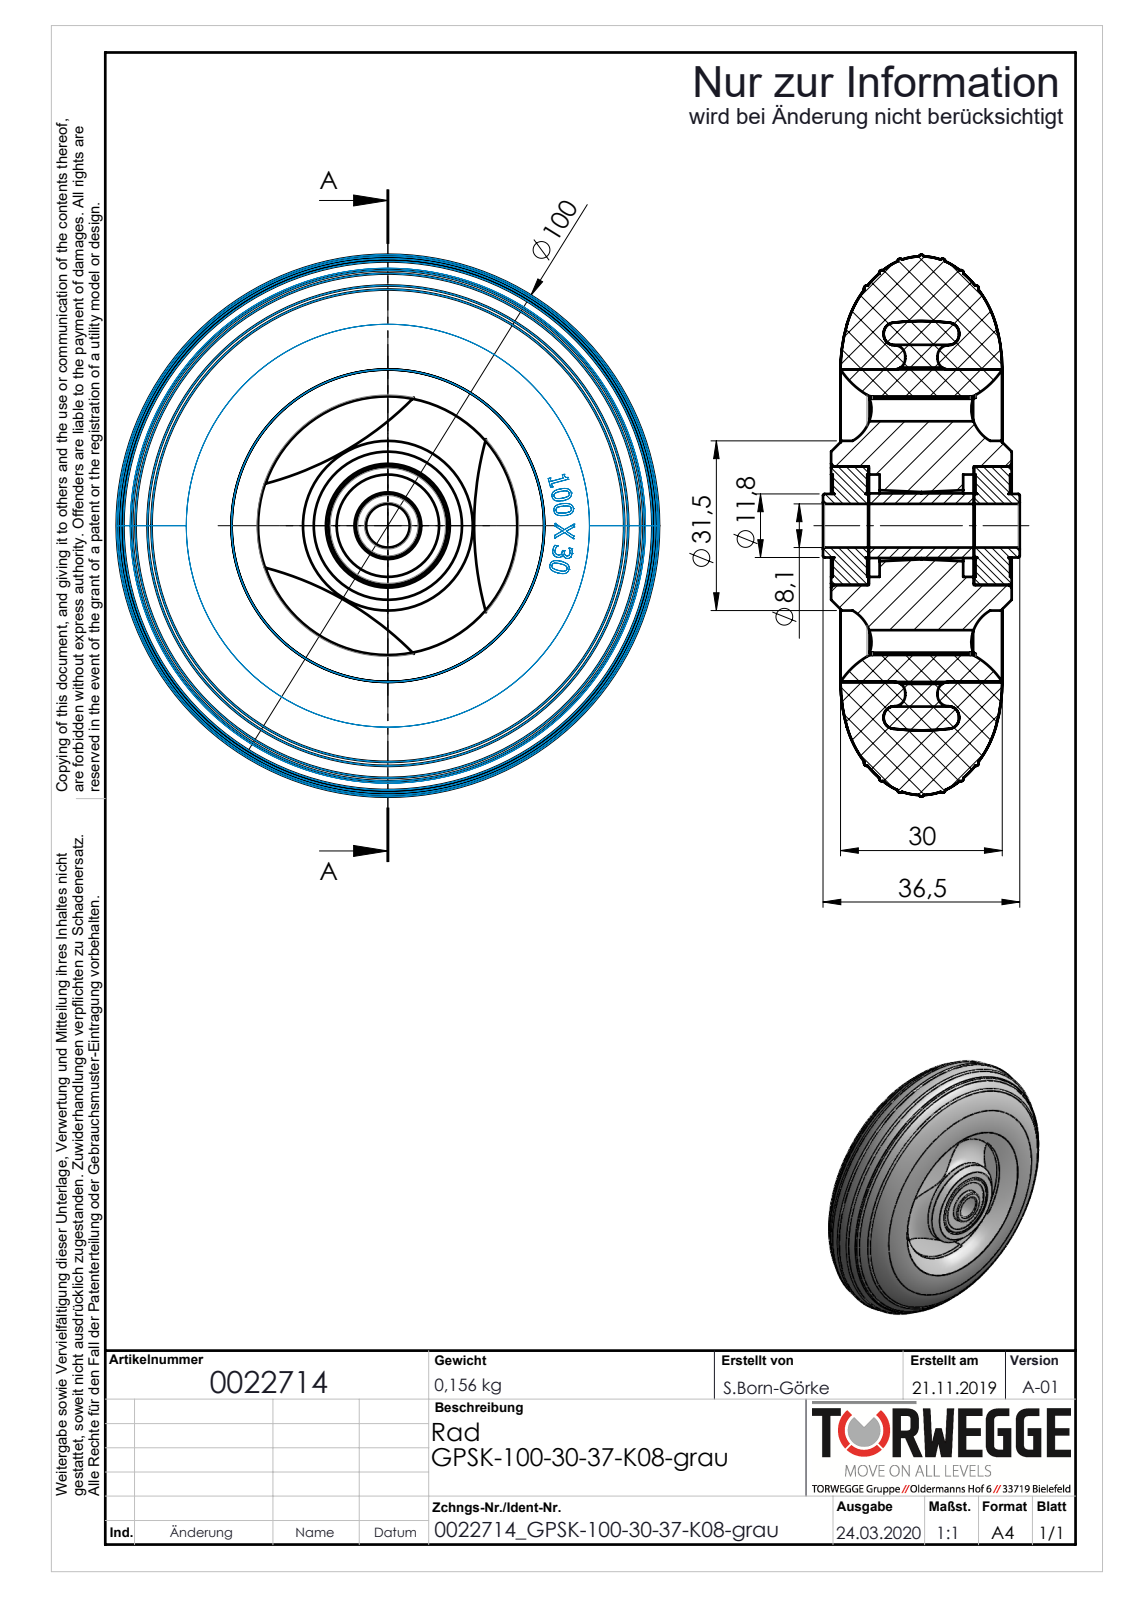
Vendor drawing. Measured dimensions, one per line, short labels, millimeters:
name: 0022714
written by: SolidWorks 2018 (AUTOMOTIVE_DESIGN)
unit: mm
bodies: 0 solids, 564 faces (108 planar, 103 cylindrical, 353 other)
size: 100.6 × 100.6 × 36.5
holes: 1× ⌀8.1, 1× ⌀19, 1× ⌀22
bosses: 1× ⌀58, 1× ⌀31.5, 1× ⌀12, 1× ⌀11.8
rounds: 24× R2.5, 3× R60, 1× R24, 1× R34
face distances: 26.5, 6.7, 7, 26.8, 19.8, 33.2, 6.4, 26.2, 9, 24.5
